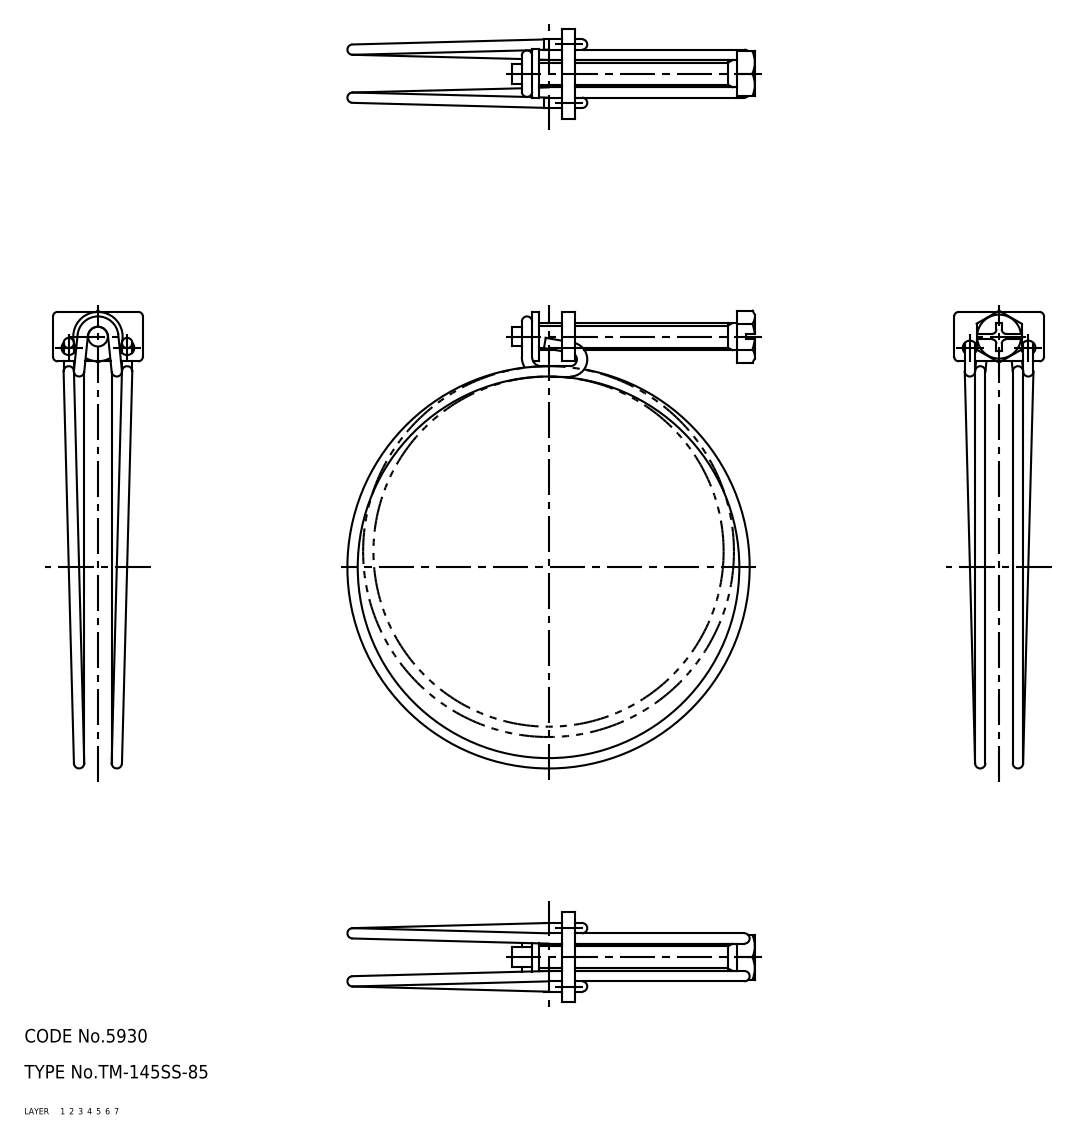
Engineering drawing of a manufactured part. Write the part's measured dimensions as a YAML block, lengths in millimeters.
part_name: "screw; holder; band; TM_145SS_85"
step_written_by: "SolidWorks 2015 (AUTOMOTIVE_DESIGN)"
units: millimeters
bodies: {solids: 3, faces: 95, planar: 31, cylindrical: 36, other: 28}
overall_size: [102.14, 90.77, 20]
volume: 4874
surface_area: 6580
round_holes:
  - {diameter: 3.2, count: 2}
  - {diameter: 6, count: 1}
round_bosses_or_shafts:
  - {diameter: 2.3, count: 8}
  - {diameter: 11, count: 1}
  - {diameter: 4.4, count: 1}
partial_cylinders:
  - {radius: 1, count: 8}
face_to_face_distances: [3, 5, 6.6, 9.6, 11, 1.6, 8, 10, 49.6, 48]
hole_center_spacings: [6.96, 13]
